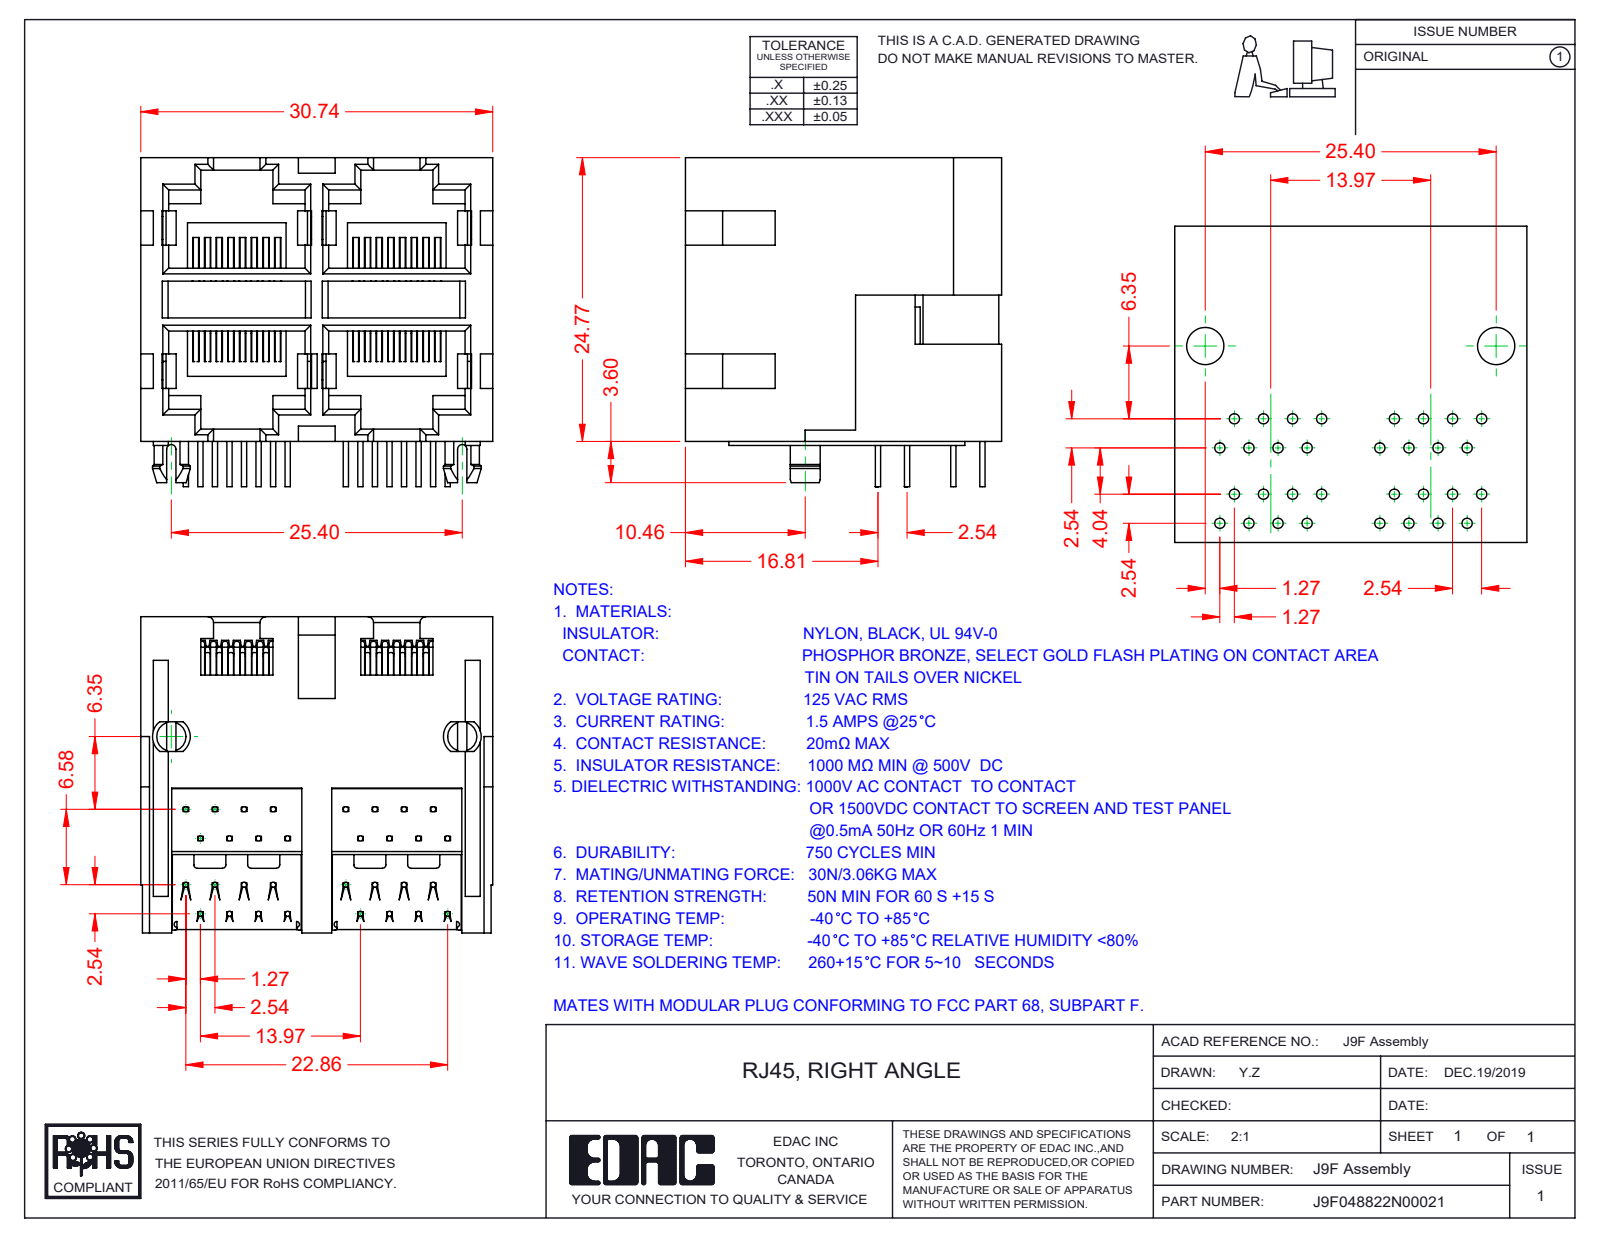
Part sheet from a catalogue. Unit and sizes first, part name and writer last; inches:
Units: inches
Overall size (bounding box): 1.21 × 1.13 × 1.087
Round bosses / shafts (diameter × count): ⌀0.018 ×144
Partial cylindrical surfaces — rounded edges, fillets, slot ends (radius × count): R0.008 ×63, R0.02 ×25, R0.012 ×9, R0.01 ×4, R0.016 ×2, R0.018 ×2, R0.059 ×2, R0.065 ×2
Main face-to-face distances: 0.55, 0.039, 0.014, 0.5, 0.591, 0.514, 0.472, 0.041, 0.536, 0.217
Volume: 0.718 in³ · Surface area: 30.65 in²
Bodies: 37 solids, 2810 faces (1899 planar, 557 cylindrical, 354 other)
Part name (STEP PRODUCT): 9F Contact Lock Upper; 9F Contact Lock Lower; 9F Contacts Lower; RJ9F048822N00021 (+2 more)
STEP written by: SolidWorks 2016 (CONFIG_CONTROL_DESIGN)
